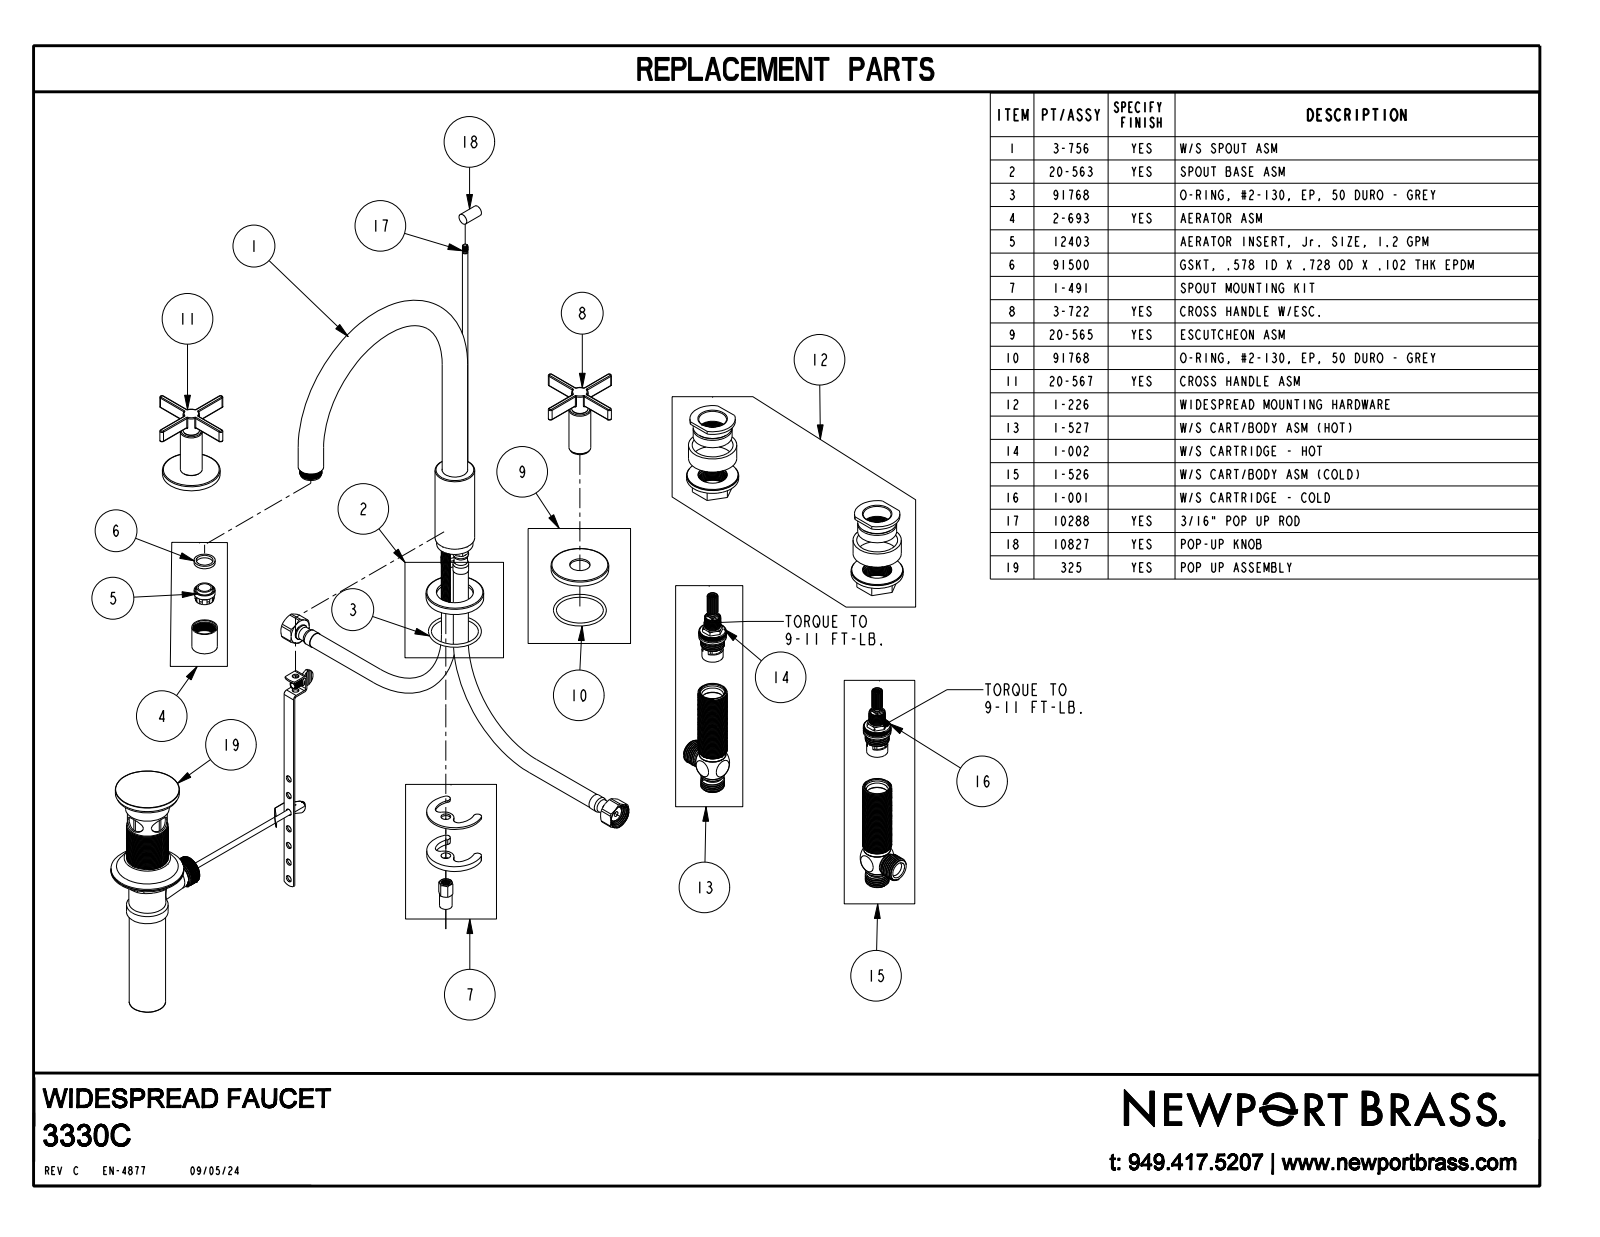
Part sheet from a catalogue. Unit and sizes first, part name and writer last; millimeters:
Units: millimetres
Overall size (bounding box): 291.9 × 279.4 × 230.2
Round holes (diameter × count): ⌀13.6 ×2
Round bosses / shafts (diameter × count): ⌀50.3 ×3, ⌀22.2 ×2, ⌀19.1 ×2, ⌀18.5 ×2, ⌀14.3 ×2, ⌀13 ×2, ⌀34.5 ×1, ⌀33.8 ×1
Partial cylindrical surfaces — rounded edges, fillets, slot ends (radius × count): R0.8 ×28, R1.9 ×8, R5 ×2
Main face-to-face distances: 5.1, 1.3, 3.8, 3.8, 203.2, 6.4, 64.8, 59.7, 58.4, 98.5
Hole centre spacings: 203.2
Volume: 306 100 mm³ · Surface area: 68 580 mm²
Bodies: 6 solids, 227 faces (51 planar, 94 cylindrical, 82 other)
Part name (STEP PRODUCT): 3330C_SW0001
STEP written by: CREO PARAMETRIC BY PTC INC, 2018400 (CONFIG_CONTROL_DESIGN)
